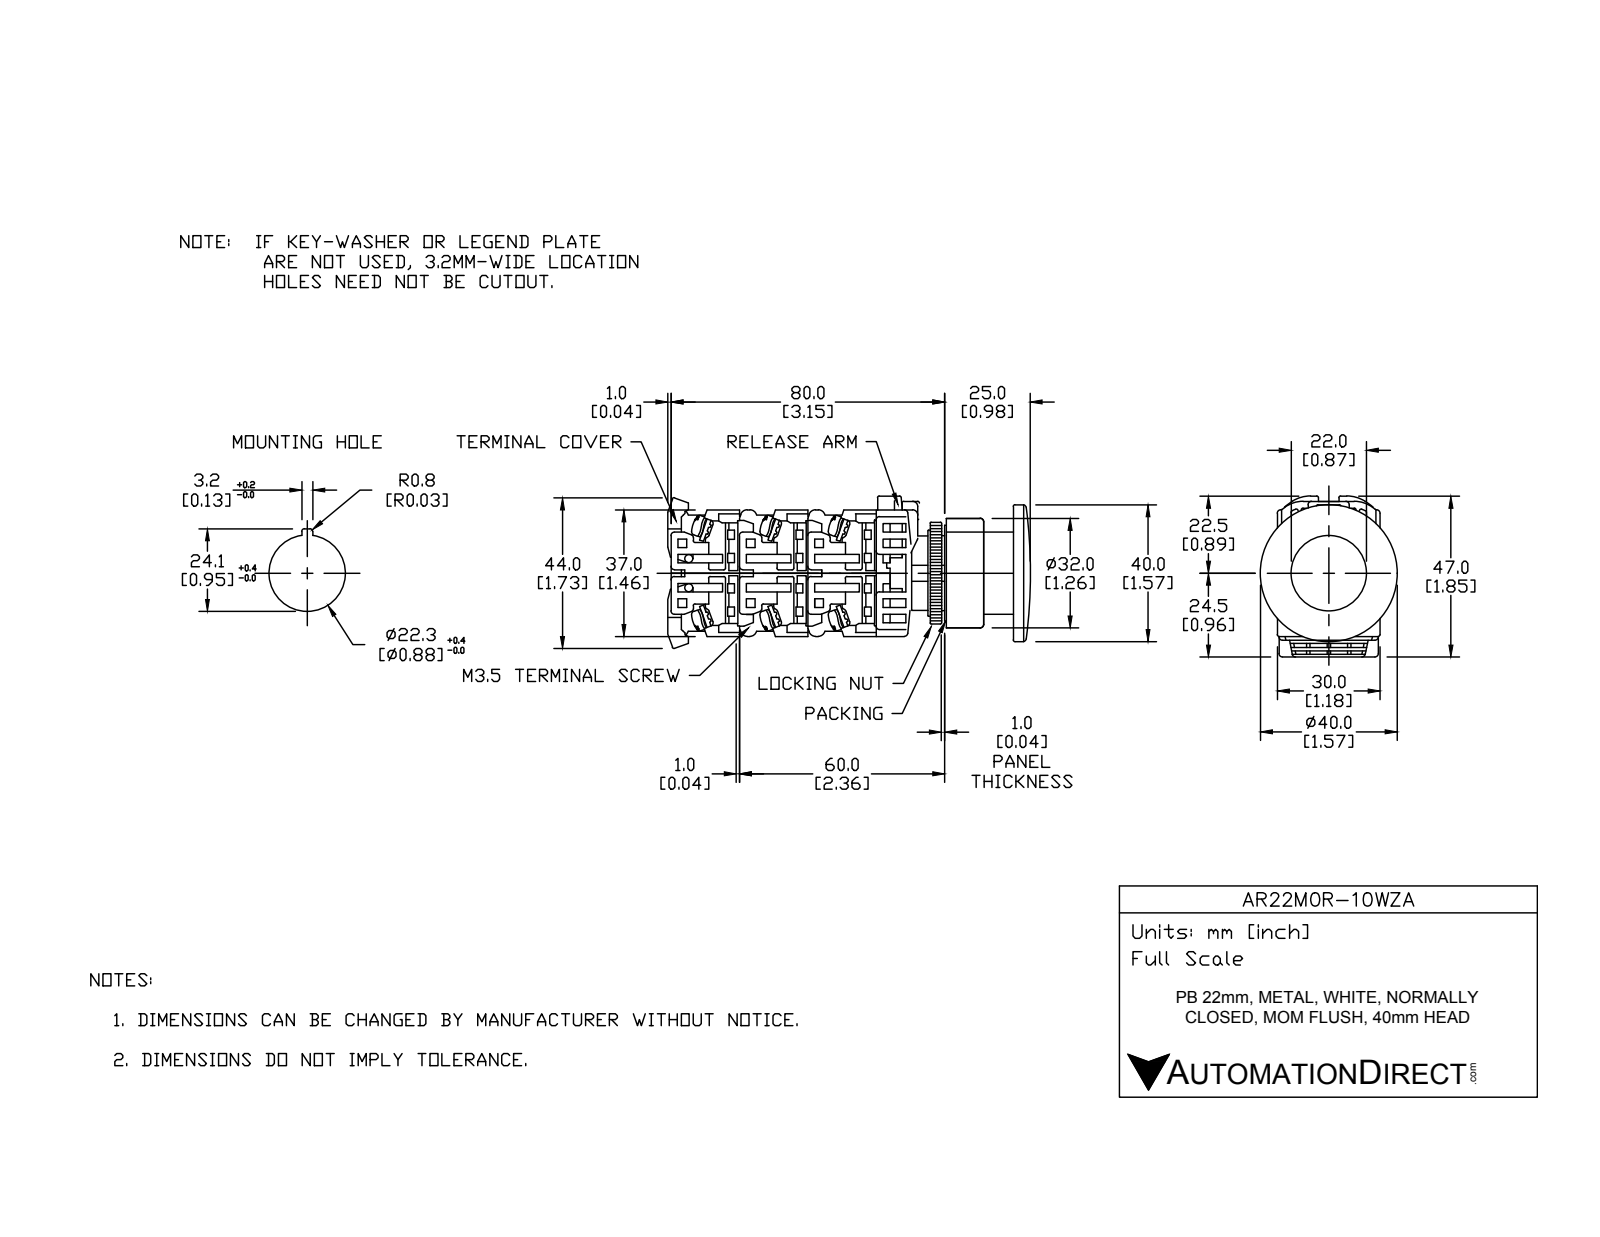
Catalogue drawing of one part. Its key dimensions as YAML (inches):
part_name: "AR22M0R-10WZA"
step_written_by: "SolidWorks 2017 (AUTOMOTIVE_DESIGN)"
units: inches
bodies: {solids: 12, faces: 304, planar: 202, cylindrical: 76, other: 26}
overall_size: [2.539, 1.693, 1.575]
volume: 2.193
surface_area: 34.15
round_holes:
  - {diameter: 0.858, count: 1}
  - {diameter: 0.866, count: 1}
  - {diameter: 0.984, count: 1}
  - {diameter: 1.22, count: 1}
round_bosses_or_shafts:
  - {diameter: 0.197, count: 2}
  - {diameter: 1.575, count: 1}
  - {diameter: 1.26, count: 1}
  - {diameter: 1.201, count: 1}
  - {diameter: 1.173, count: 1}
  - {diameter: 0.945, count: 1}
  - {diameter: 0.937, count: 1}
  - {diameter: 0.856, count: 1}
partial_cylinders:
  - {radius: 0.02, count: 23}
  - {radius: 0.069, count: 4}
  - {radius: 0.197, count: 4}
  - {radius: 0.157, count: 2}
  - {radius: 0.653, count: 1}
  - {radius: 0.693, count: 1}
face_to_face_distances: [0.039, 0.394, 1.122, 0.709, 1.516, 0.827, 0.118, 0.079, 1.142, 0.295]
